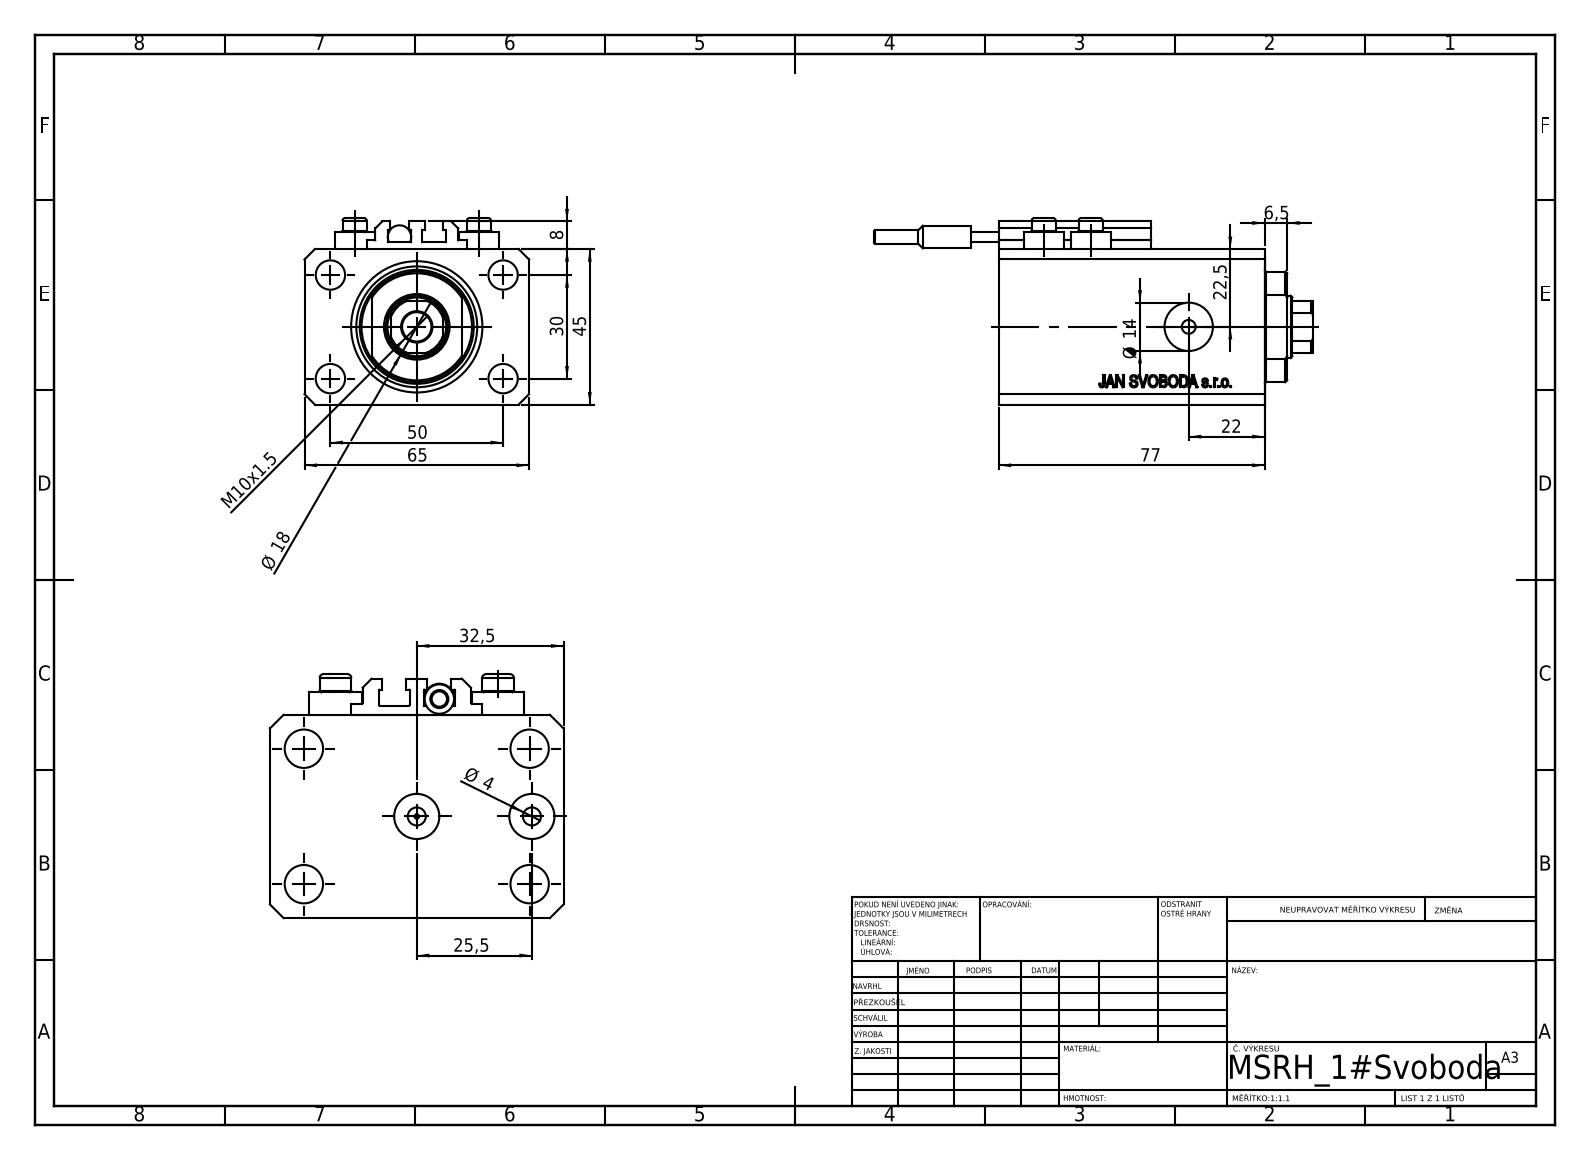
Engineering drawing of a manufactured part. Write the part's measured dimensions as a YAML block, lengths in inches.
part_name: "ALLEN BOLT V250CE; V250CE_C_VCP; SWITCH_V250CE; V250CE_VC_C (+1 more)"
step_written_by: "SolidWorks 2019 (CONFIG_CONTROL_DESIGN)"
units: inches
bodies: {solids: 9, faces: 1068, planar: 520, cylindrical: 98, other: 450}
overall_size: [5, 2.559, 2.126]
volume: 13.02
surface_area: 91.54
round_holes:
  - {diameter: 0.157, count: 8}
  - {diameter: 0.335, count: 5}
  - {diameter: 0.394, count: 2}
  - {diameter: 0.551, count: 2}
  - {diameter: 0.049, count: 1}
  - {diameter: 0.709, count: 1}
  - {diameter: 0.984, count: 1}
  - {diameter: 1.496, count: 1}
round_bosses_or_shafts:
  - {diameter: 0.457, count: 4}
  - {diameter: 0.276, count: 4}
  - {diameter: 0.268, count: 1}
  - {diameter: 0.256, count: 1}
  - {diameter: 0.157, count: 1}
partial_cylinders:
  - {radius: 0.008, count: 10}
  - {radius: 0.335, count: 1}
  - {radius: 0.63, count: 1}
face_to_face_distances: [1.772, 2.559, 0.551, 3.031, 2.48, 0.118, 1.85, 0.272, 2.209, 2.76]
hole_center_spacings: [1.148, 0.535, 0.591, 1.181, 1.417, 1.515, 1.969, 2.074]
